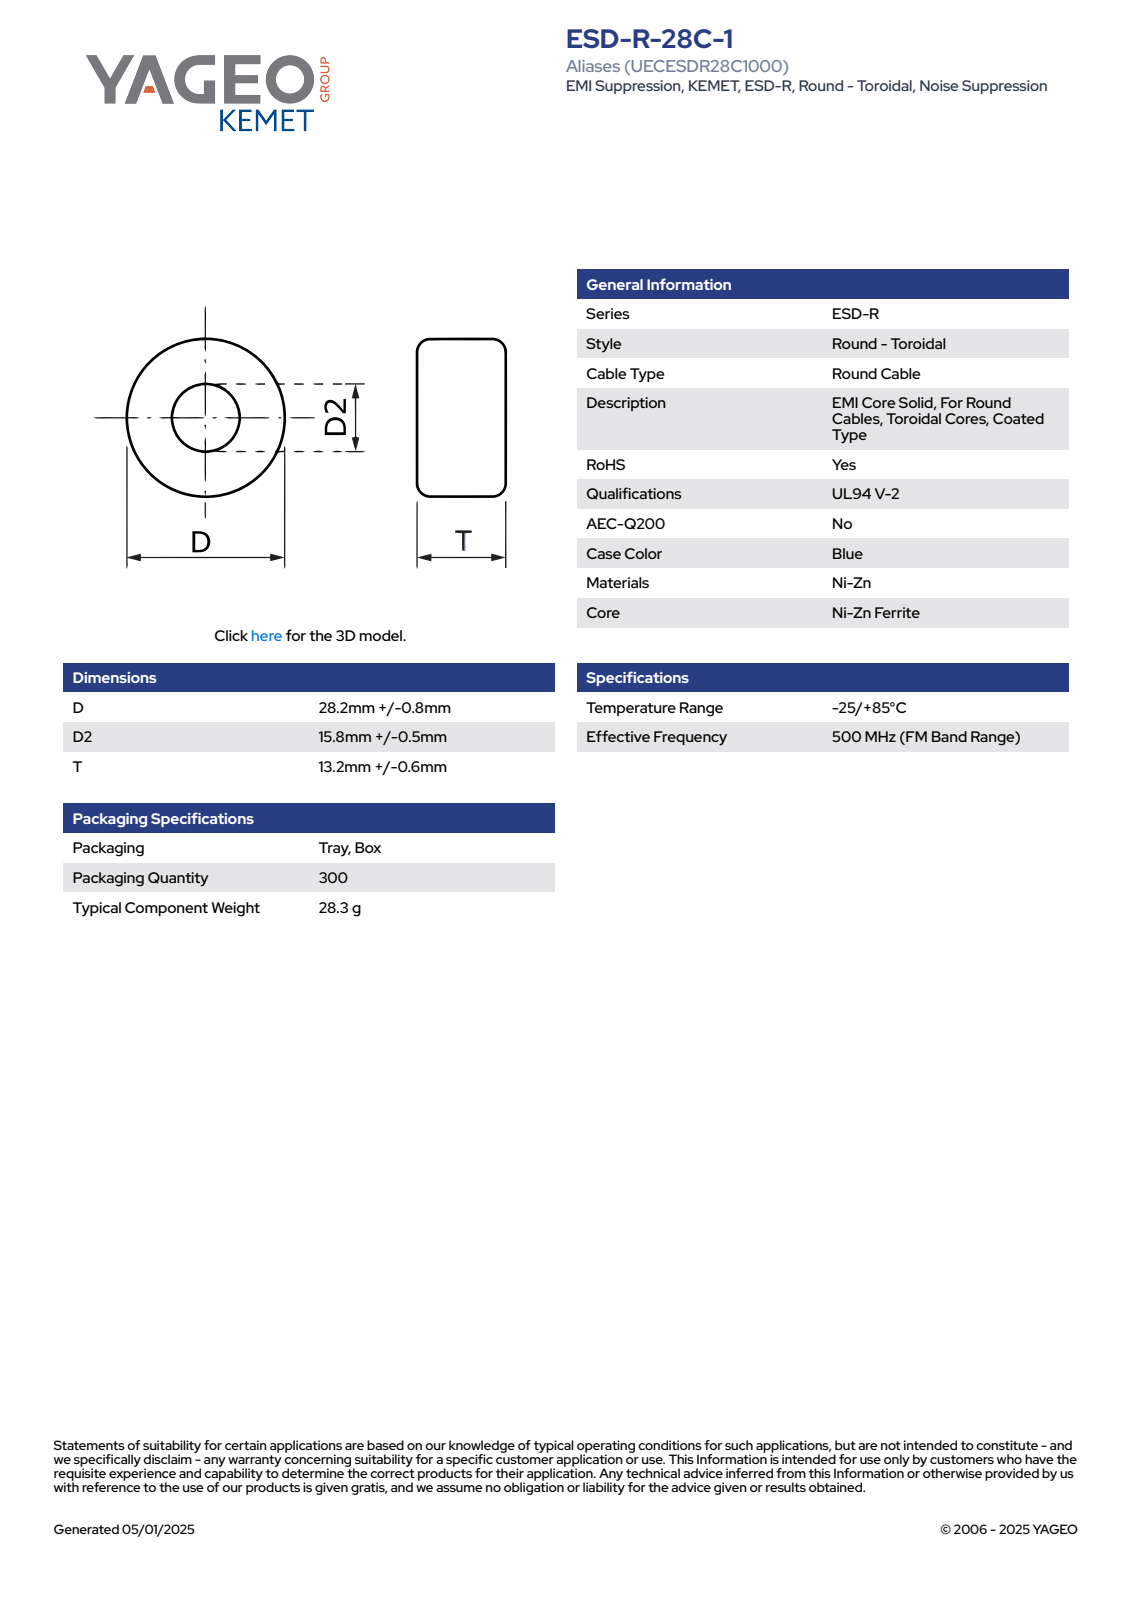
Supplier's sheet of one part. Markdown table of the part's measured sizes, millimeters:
| quantity | value |
| --- | --- |
| part name | EC_KBC_D29D215.8T13.8 |
| STEP written by | SolidWorks 2021 (AUTOMOTIVE_DESIGN) |
| units | millimeters |
| bodies | 1 solid, 66 faces (24 planar, 7 cylindrical, 35 other) |
| overall size | 29.01 × 29 × 13.8 |
| volume | 6 377 mm³ |
| surface area | 2 807 mm² |
| round holes (diameter × count) | 15.8 × 1 |
| round bosses / shafts (diameter × count) | 29 × 1 |
| partial cylindrical surfaces (radius × count) | 14.51 × 1 |
| main face-to-face distances | 13.8, 6.05, 7.75, 1.7, 0.32, 6.37, 7.43, 1.38, 1.06, 7.11 |
